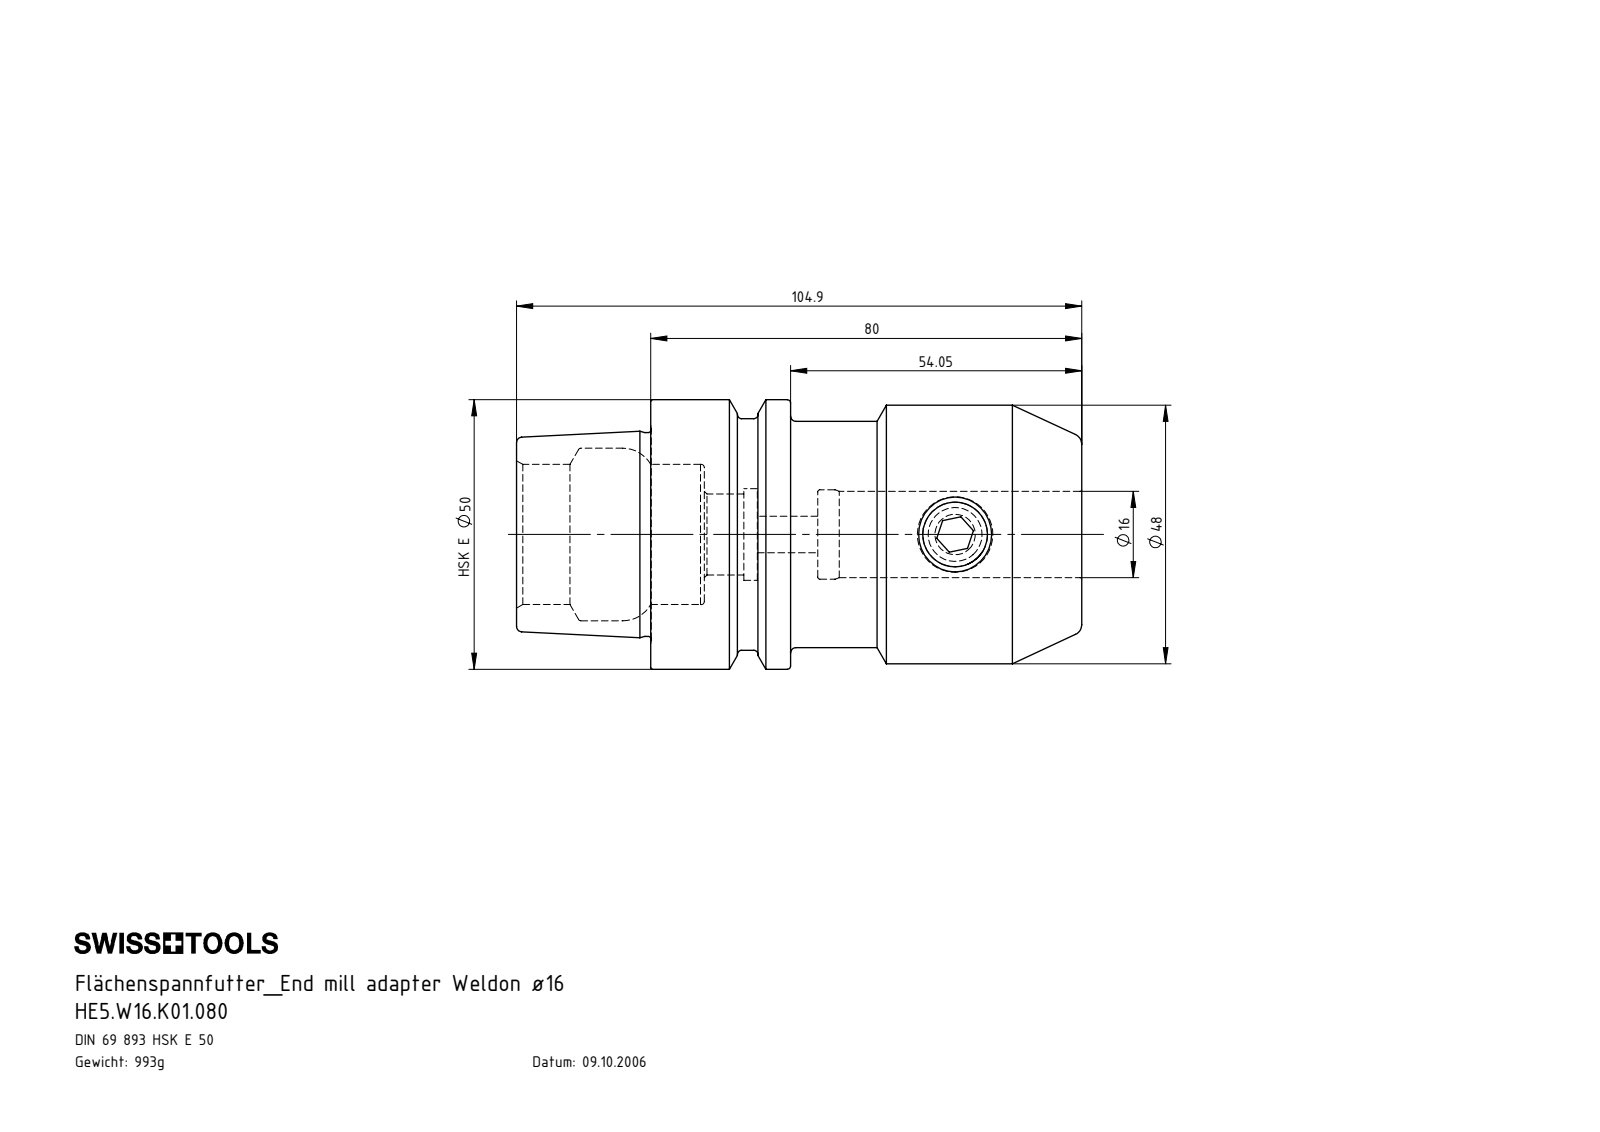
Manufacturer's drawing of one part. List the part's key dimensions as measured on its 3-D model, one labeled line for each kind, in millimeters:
Part name (STEP PRODUCT): W16-ER1.001.016; HE5.W16.K01.080; HE5-W16.K01.080_B_Fertigbearbeitung
STEP written by: SolidWorks 2017 (AUTOMOTIVE_DESIGN)
Units: millimetres
Bodies: 2 solids, 113 faces (19 planar, 32 cylindrical, 62 other)
Overall size (bounding box): 104.9 × 50 × 50
Volume: 126 541 mm³ · Surface area: 26 831 mm²
Round holes (diameter × count): ⌀6.8 ×1, ⌀12 ×1, ⌀15 ×1, ⌀16 ×1, ⌀16.6 ×1, ⌀17 ×1, ⌀26 ×1, ⌀32 ×1
Round bosses / shafts (diameter × count): ⌀50 ×1, ⌀48 ×1, ⌀42.95 ×1, ⌀42 ×1, ⌀37.81 ×1, ⌀14 ×1
Main face-to-face distances: 80, 25.95, 54.05, 24.9, 50.85, 104.9, 34.85, 9.95, 16, 70.05
